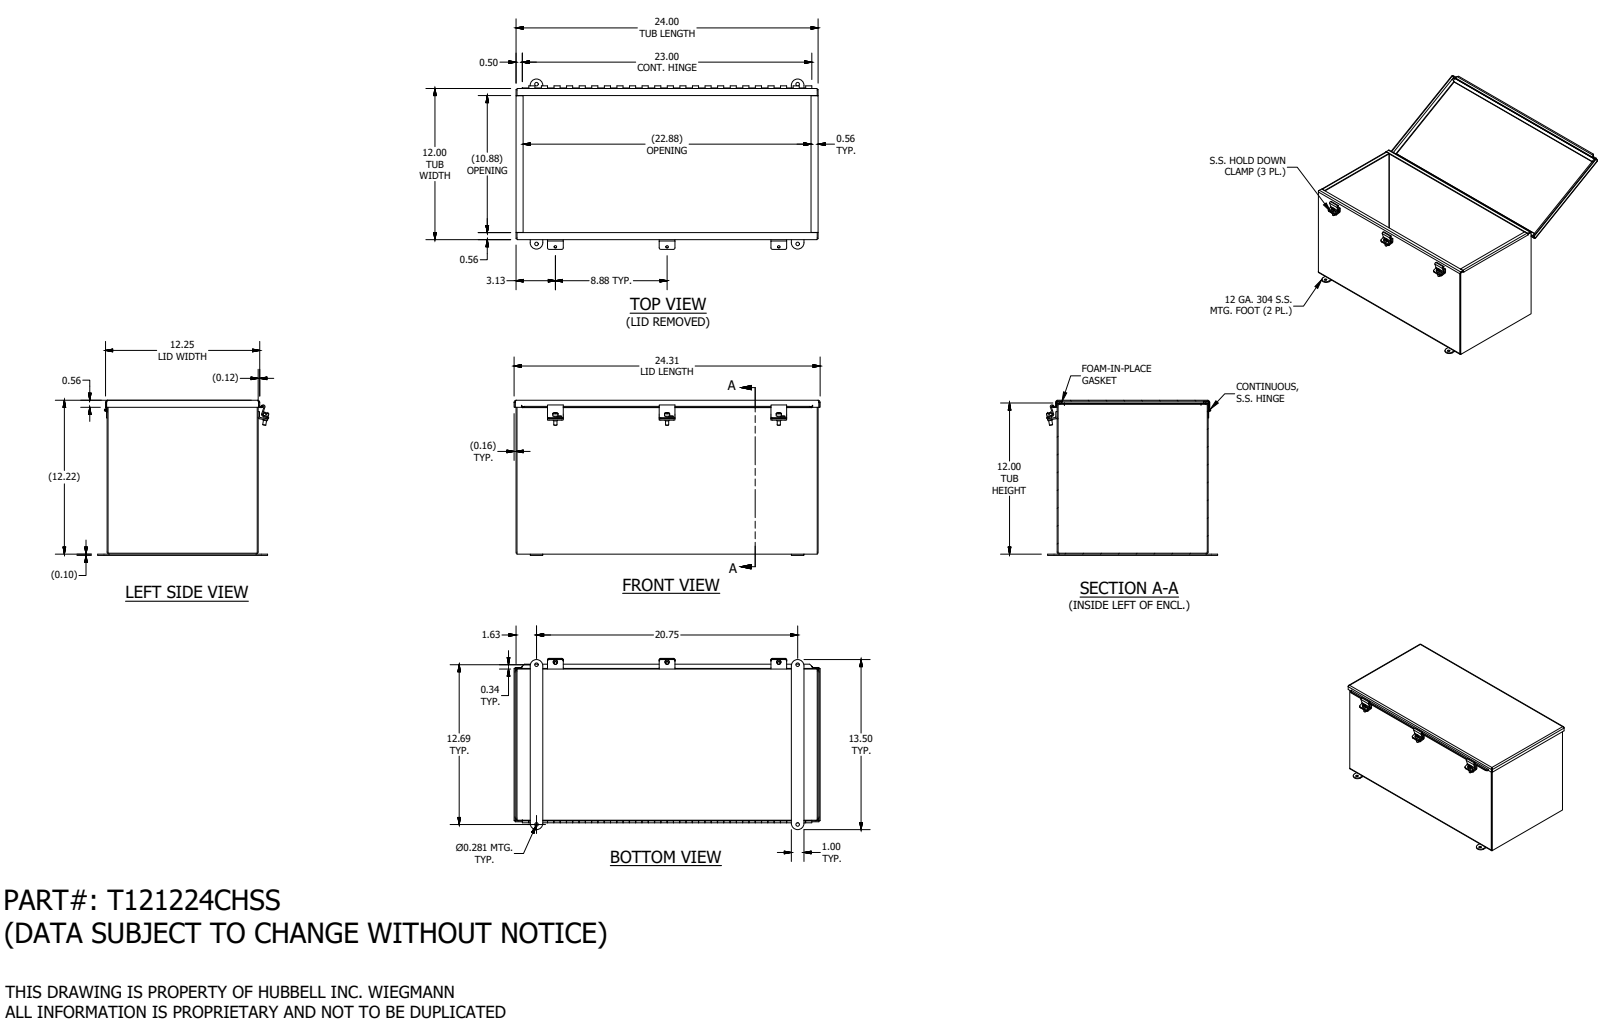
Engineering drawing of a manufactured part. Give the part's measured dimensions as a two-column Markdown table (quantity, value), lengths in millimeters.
| quantity | value |
| --- | --- |
| part name | T121224CHSS |
| STEP written by | SolidWorks 2019 (AUTOMOTIVE_DESIGN) |
| units | millimeters |
| bodies | 19 solids, 591 faces (355 planar, 197 cylindrical, 39 other) |
| overall size | 617.6 × 345.4 × 313 |
| volume | 2 009 000 mm³ |
| surface area | 2 112 000 mm² |
| round holes (diameter × count) | 2.8 × 6, 7.1 × 4, 5 × 3, 2.9 × 1 |
| round bosses / shafts (diameter × count) | 10.4 × 3, 8.7 × 3, 6.4 × 3, 5.1 × 1, 2.5 × 1 |
| partial cylindrical surfaces (radius × count) | 3.2 × 12, 2.4 × 11, 4.3 × 11, 2.2 × 8, 3.4 × 6, 6.1 × 4, 12.7 × 4, 1.6 × 3 |
| main face-to-face distances | 1.9, 302.9, 308.5, 301, 304.8, 310.3, 306.6, 607.7, 605.8, 609.6 |
| hole center spacings | 225.4, 19.1, 225.4, 322.2, 450.9, 527.1, 617.8, 206.4 |
